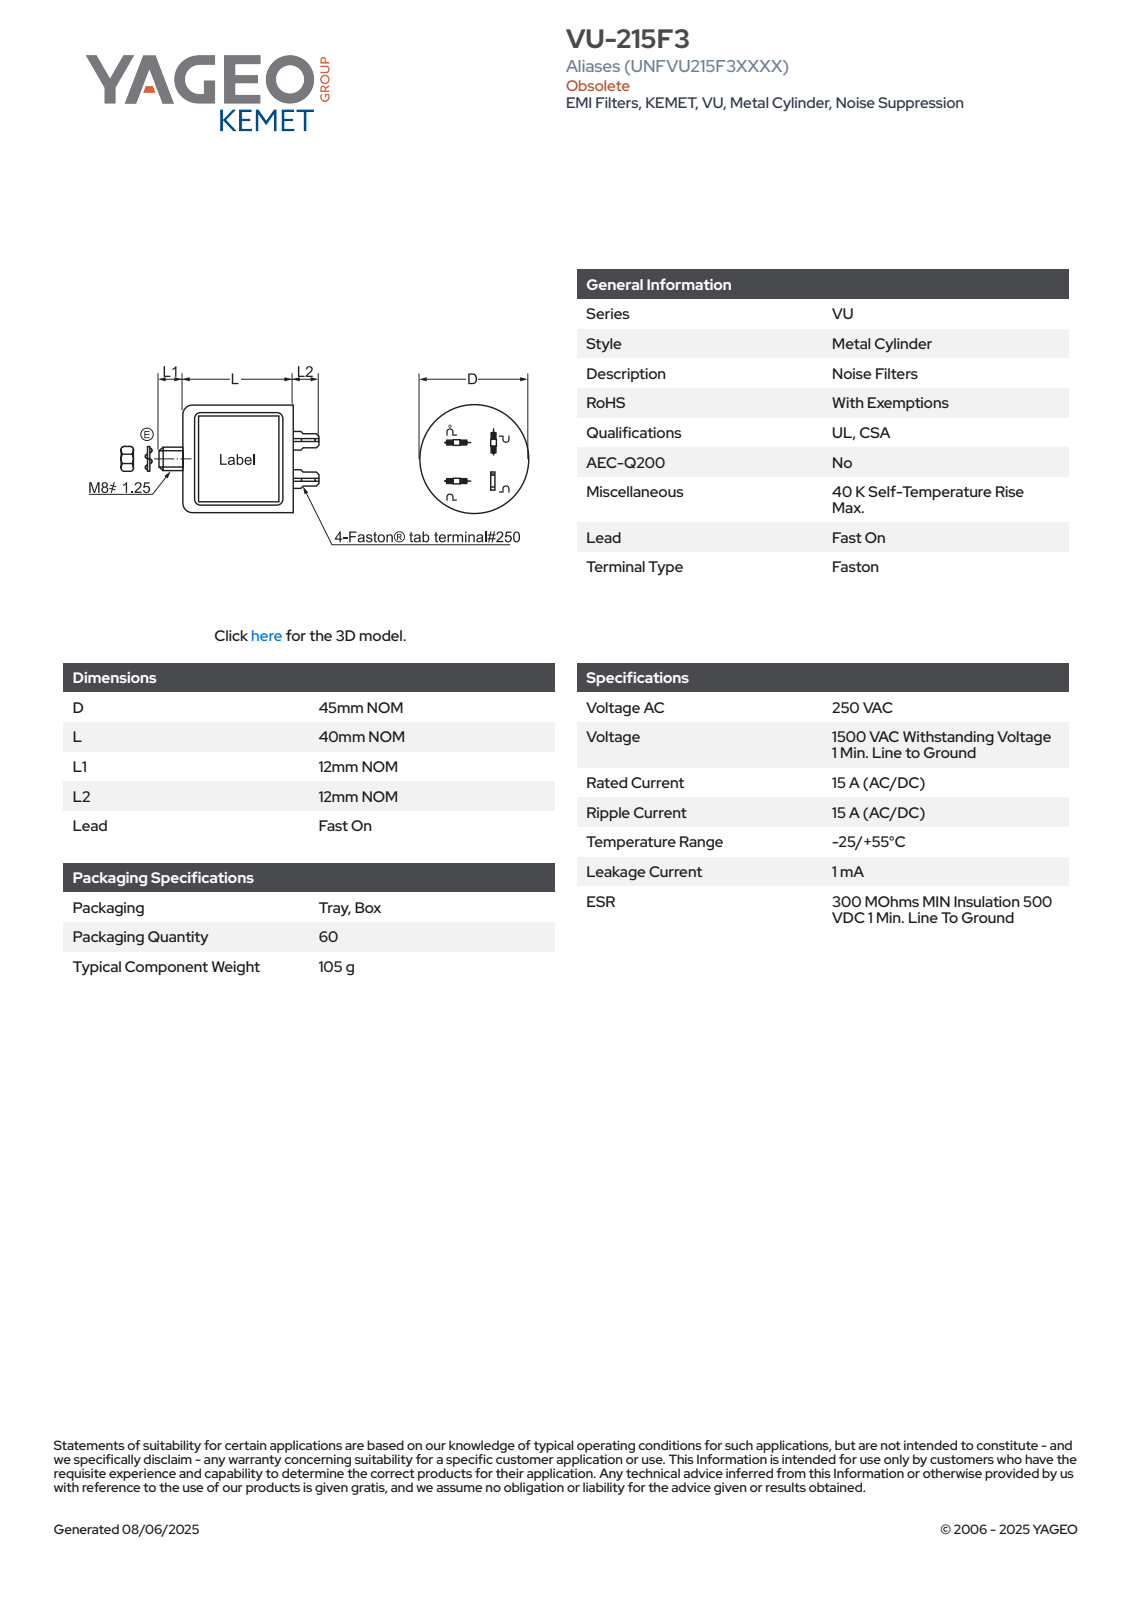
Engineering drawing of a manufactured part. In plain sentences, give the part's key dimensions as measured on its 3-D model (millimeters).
The part is named "ENF_VUF_D45L40L112L212". Its 3-D file was written by "SolidWorks 2014 (AUTOMOTIVE_DESIGN)". It is 1 solid with 139 faces: 61 planar, 45 cylindrical and 33 other. Overall it measures 64 by 45 by 45 millimeters. Its volume is 64 757 cubic millimeters and its surface area 10 002 square millimeters. Round holes: 3 of diameter 1.1. Round bosses or shafts: 1 of diameter 45, 1 of diameter 8. Partial cylindrical surfaces (rounded edges, fillets, slot ends): 18 of radius 0.3, 1 of radius 22.49. The main face-to-face distances are 40, 1.5, 14.5, 13, 16, 12, 52, 64, 16.96, 16.93. The hole center spacings are 17.
